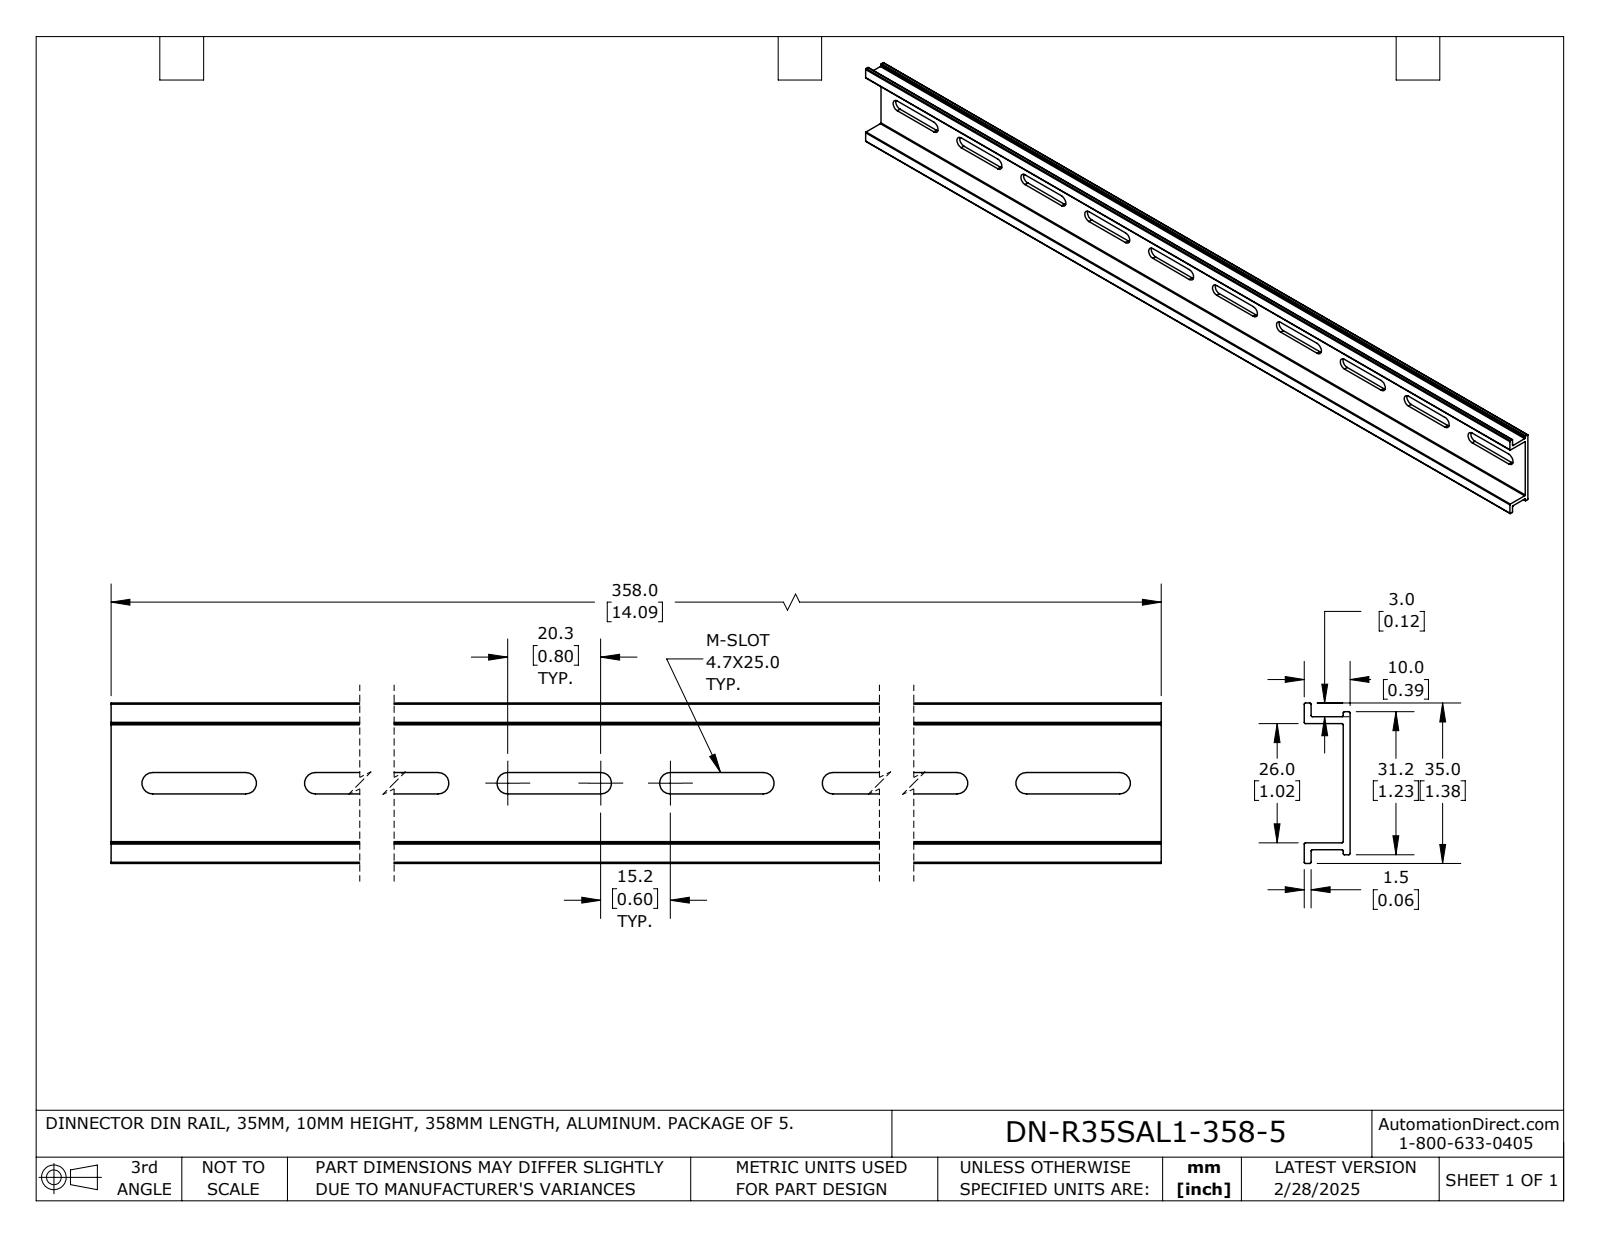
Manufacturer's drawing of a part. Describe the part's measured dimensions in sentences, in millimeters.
The part is named "DN-R35SAL1-358-5_Default". Its 3-D file was written by "SolidWorks 2024 (CONFIG_CONTROL_DESIGN)". It is 1 solid with 74 faces: 38 planar, 36 cylindrical and 0 other. Overall it measures 358 by 35 by 10 millimeters. Its volume is 27 392 cubic millimeters and its surface area 37 960 square millimeters. Partial cylindrical surfaces (rounded edges, fillets, slot ends): 20 of radius 2.35, 16 of radius 0.27. The main face-to-face distances are 1.5, 27.5, 8.5, 26, 10, 29, 7, 1.1, 2.6, 28.6.
